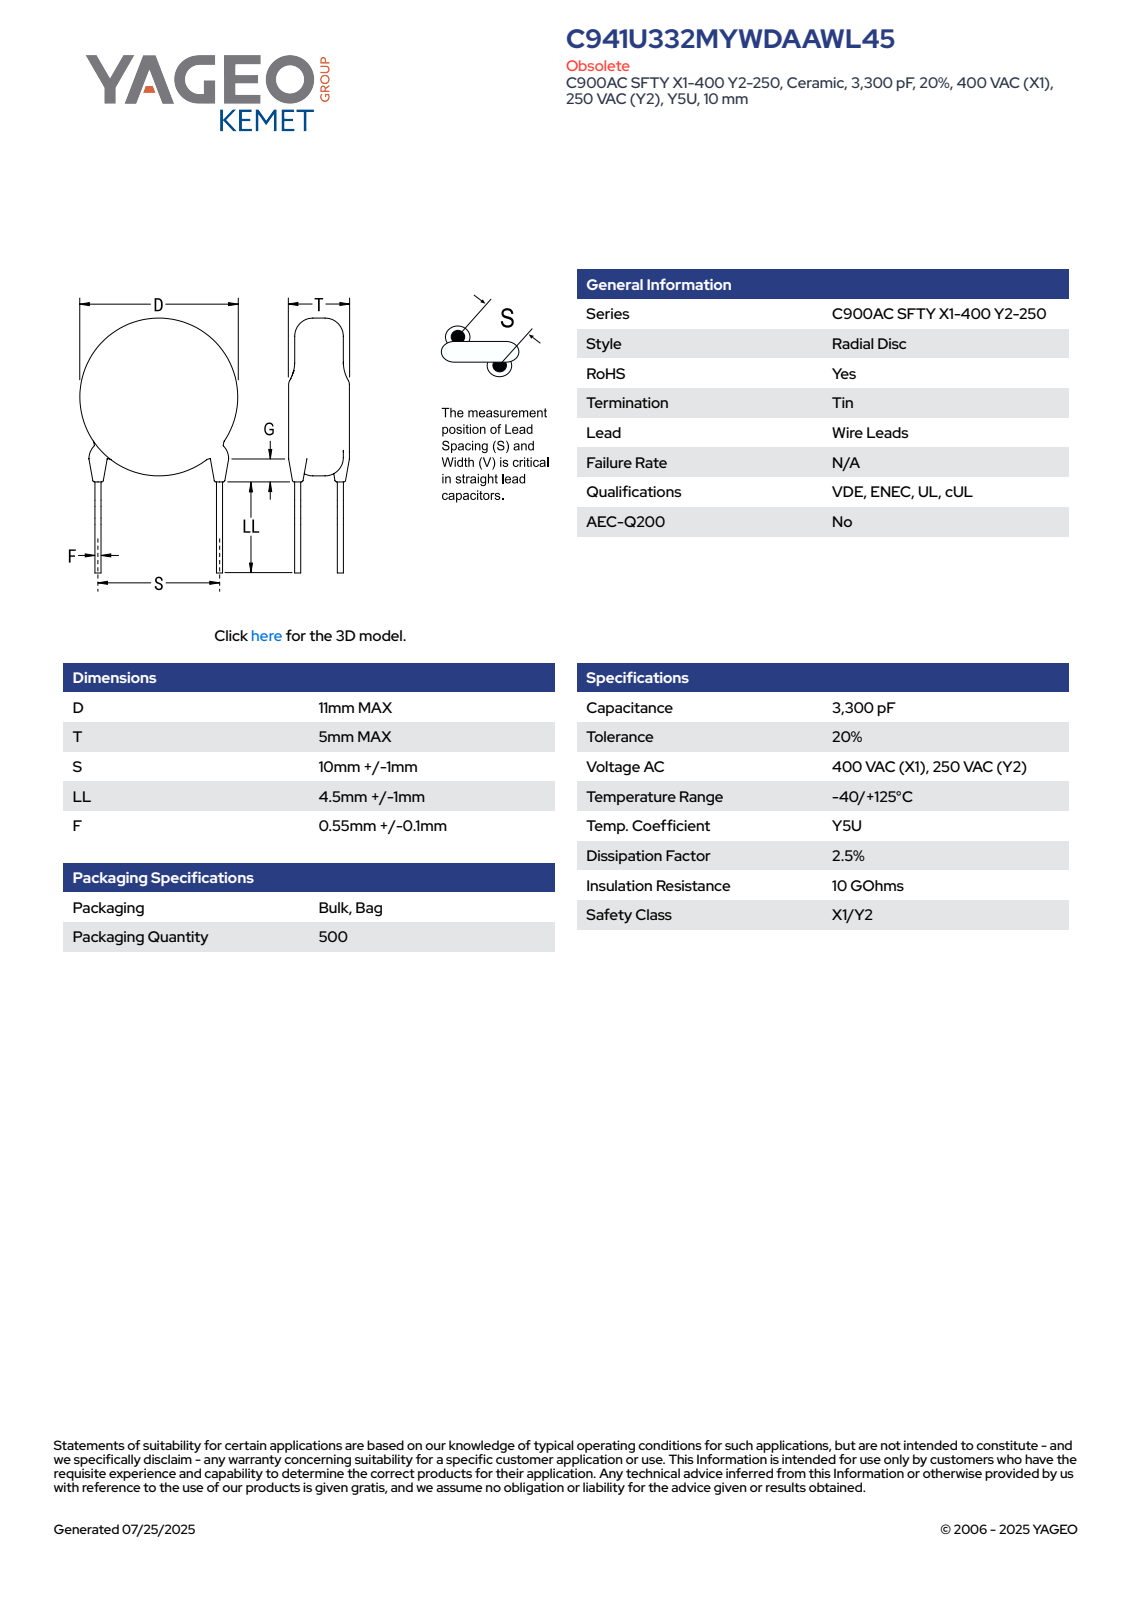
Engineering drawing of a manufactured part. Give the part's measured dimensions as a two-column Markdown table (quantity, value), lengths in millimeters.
| quantity | value |
| --- | --- |
| part name | CCD_STC900_D11T5S10LL5.5F0.65G3 |
| STEP written by | SolidWorks 2014 (AUTOMOTIVE_DESIGN) |
| units | millimeters |
| bodies | 4 solids, 83 faces (61 planar, 6 cylindrical, 16 other) |
| overall size | 16.85 × 11 × 5 |
| volume | 468 mm³ |
| surface area | 377 mm² |
| round bosses / shafts (diameter × count) | 0.65 × 2, 11 × 1 |
| main face-to-face distances | 5, 1.27, 11.98, 10.71, 0.35, 1.03, 5.19, 0.79, 3.77, 3.92 |
